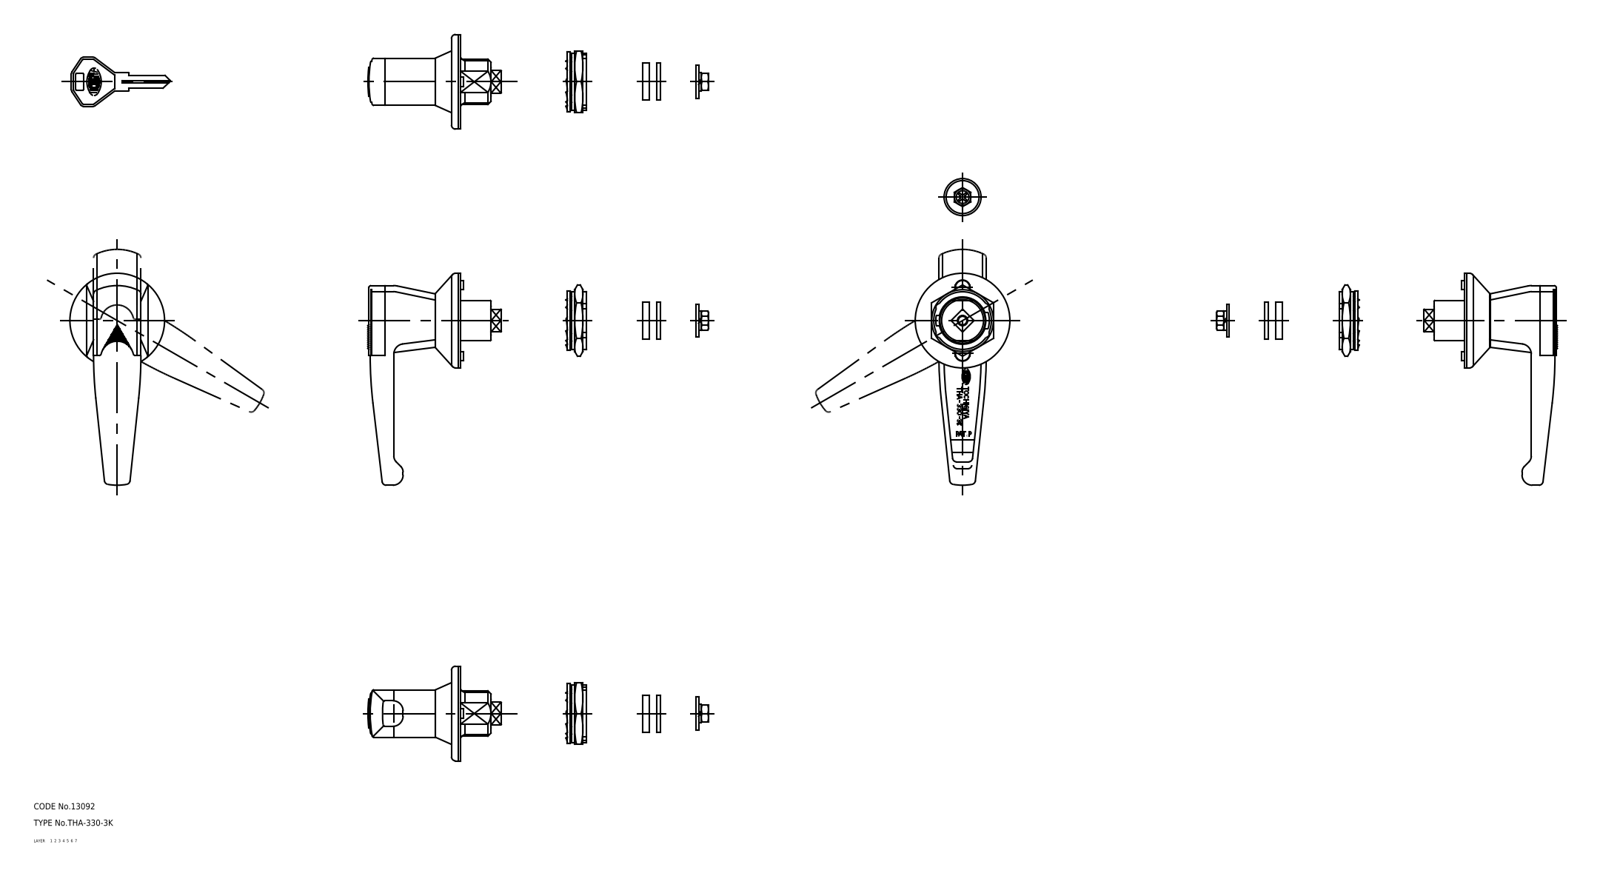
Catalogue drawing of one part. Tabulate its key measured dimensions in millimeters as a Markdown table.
| quantity | value |
| --- | --- |
| part name | key; washer_D; washer_C; washer_B (+8 more) |
| STEP written by | CADfix (AUTOMOTIVE_DESIGN) |
| units | millimeters |
| bodies | 11 solids, 379 faces (0 planar, 0 cylindrical, 379 other) |
| overall size | 129.14 × 103 × 46 |
| volume | 51 816 mm³ |
| surface area | 27 021 mm² |
